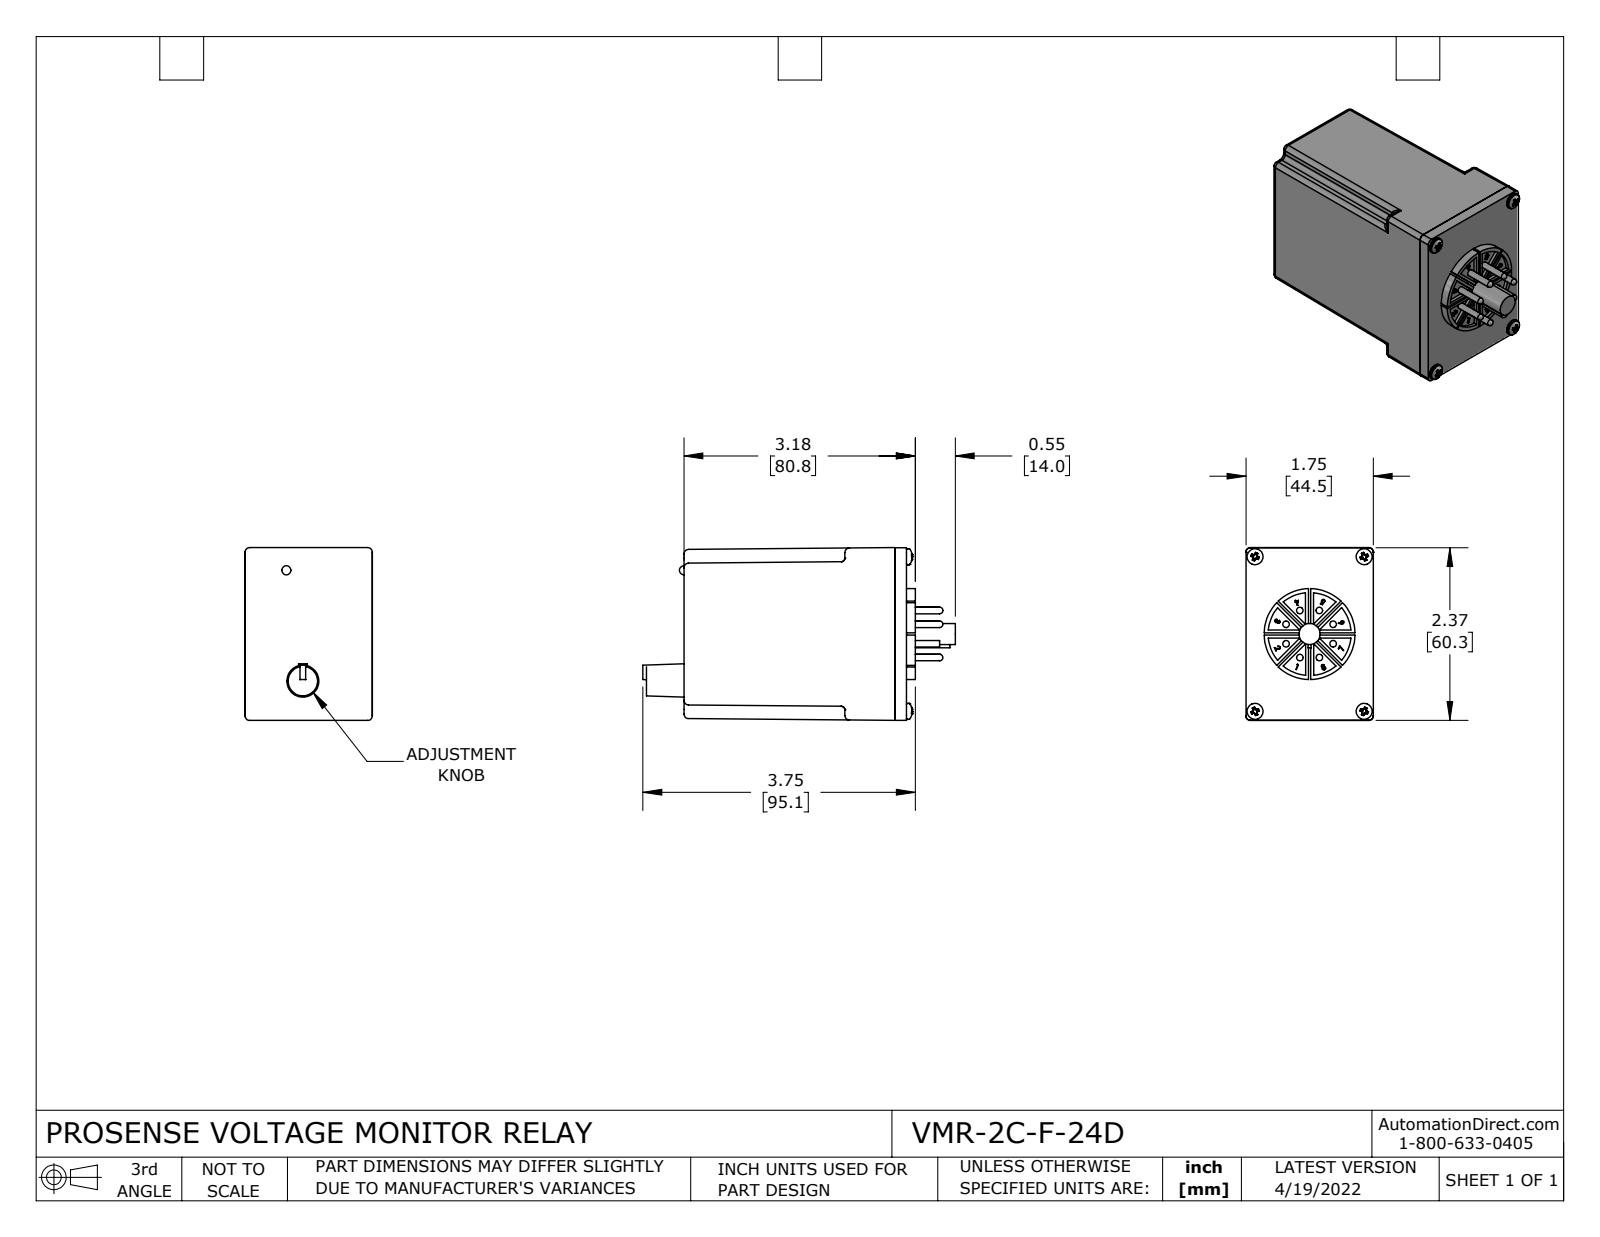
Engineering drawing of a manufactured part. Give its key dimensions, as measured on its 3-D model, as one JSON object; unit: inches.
{"part_name": "VMR-2C-F-24D", "step_written_by": "SolidWorks 2021 (CONFIG_CONTROL_DESIGN)", "units": "inches", "bodies": {"solids": 17, "faces": 542, "planar": 221, "cylindrical": 164, "other": 157}, "overall_size": [4.295, 2.375, 1.75], "volume_in3": 12.33, "surface_area_in2": 45.79, "round_holes": [[0.125, 4]], "round_bosses_or_shafts": [[0.09, 8], [0.219, 4], [1.25, 1], [0.29, 1]], "partial_cylinders_radius": [[0.063, 32], [0.005, 8], [0.05, 4], [0.57, 1]], "face_to_face_distances": [2.9, 0.16, 3.06, 0.07, 0.23, 3.13, 0.188, 0.05, 0.12, 0.28], "hole_center_spacings": [1.5, 2.125, 2.601]}
